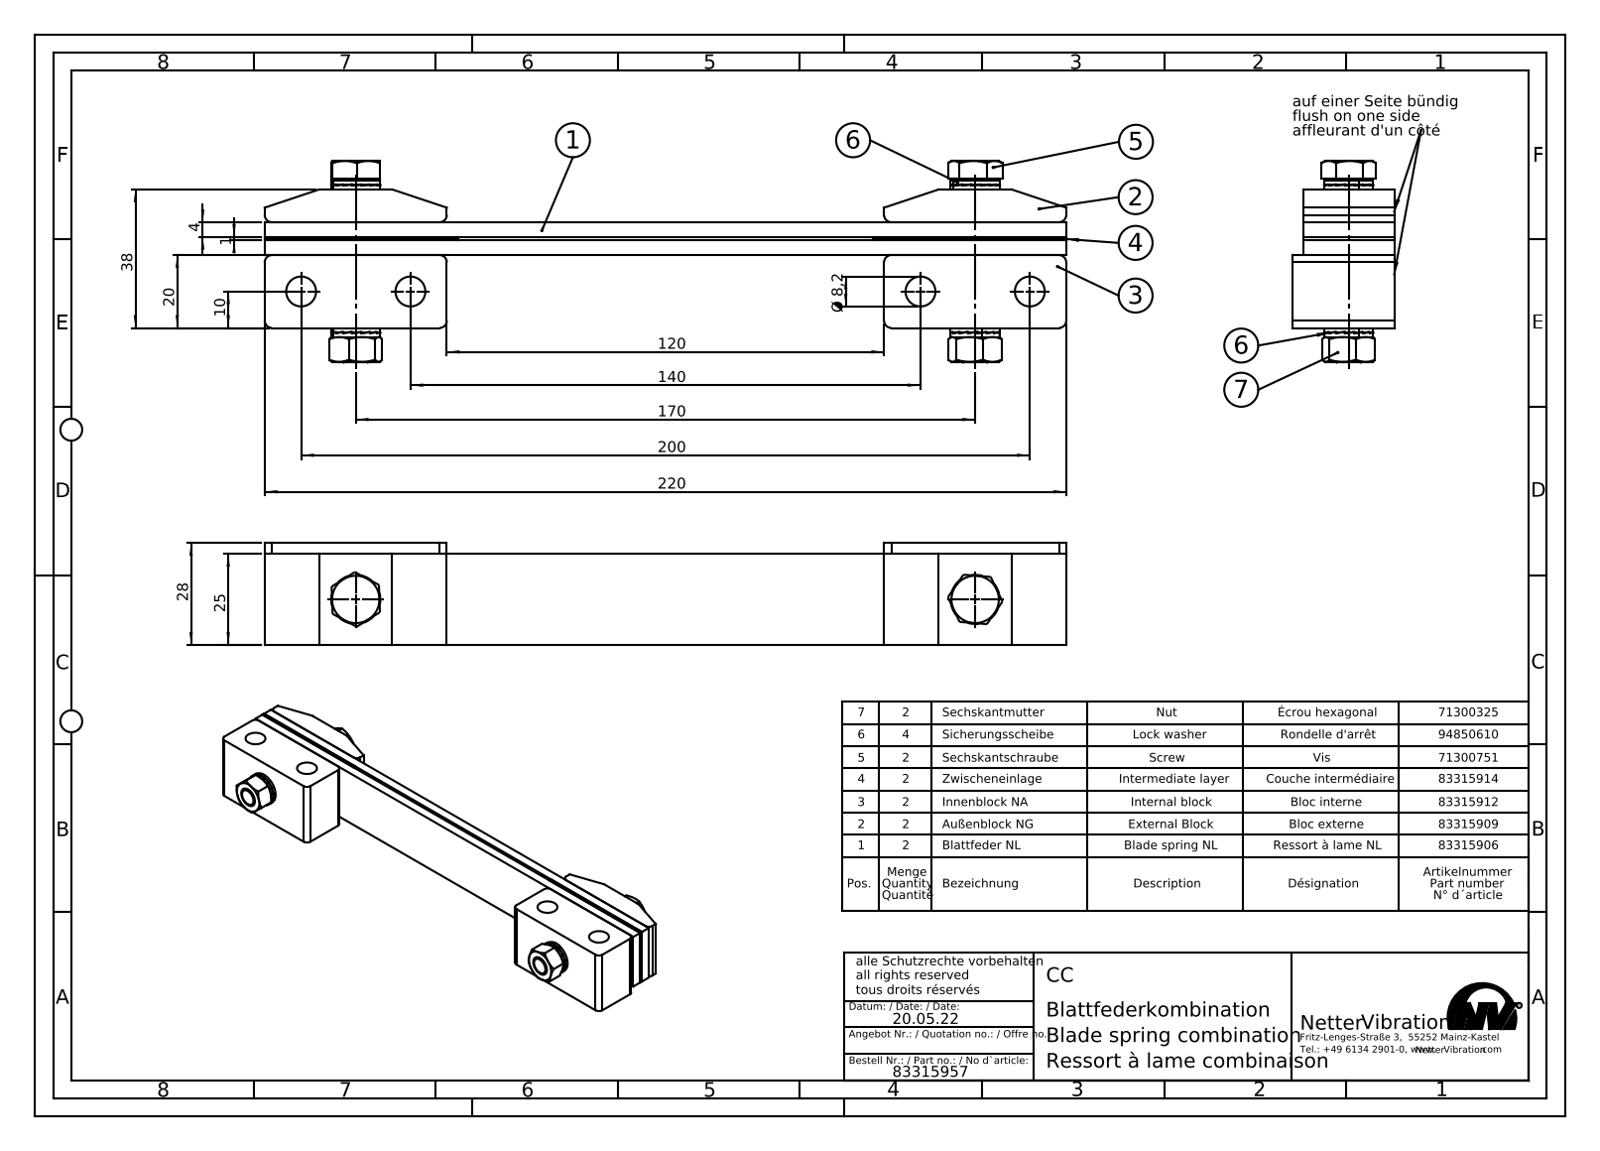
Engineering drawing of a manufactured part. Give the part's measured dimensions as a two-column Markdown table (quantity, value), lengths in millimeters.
| quantity | value |
| --- | --- |
| part name | Blattfederkombination CC # 83315971 |
| STEP written by | SolidWorks 2015 (AUTOMOTIVE_DESIGN) |
| units | millimeters |
| bodies | 16 solids, 686 faces (554 planar, 80 cylindrical, 52 other) |
| overall size | 220 × 55.3 × 28 |
| volume | 119 984 mm³ |
| surface area | 59 765 mm² |
| round holes (diameter × count) | 8.2 × 6, 6.8 × 2, 8 × 2, 8.5 × 2, 8.7 × 2 |
| round bosses / shafts (diameter × count) | 13.5 × 2, 13 × 2 |
| partial cylindrical surfaces (radius × count) | 2 × 12 |
| main face-to-face distances | 4, 5, 9, 1, 25, 29, 24, 20, 3, 28 |
| hole center spacings | 170, 30, 140, 200 |
